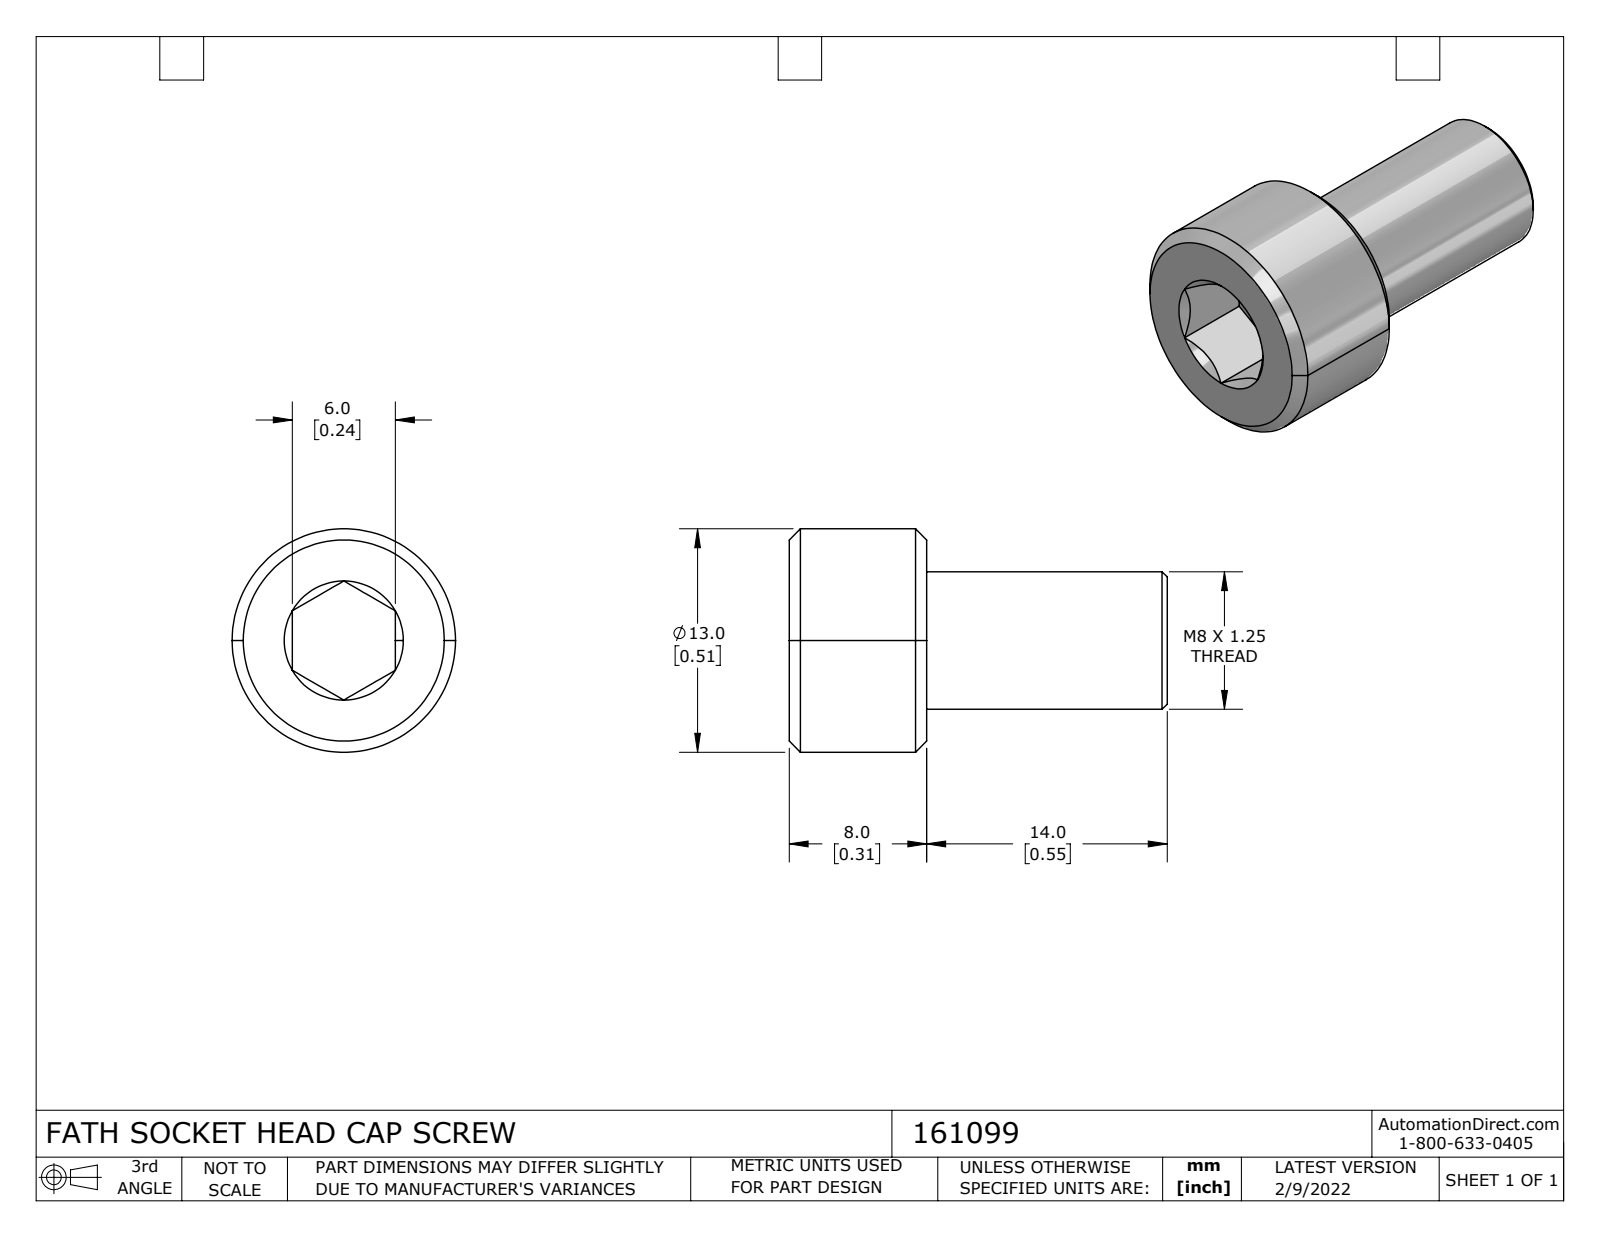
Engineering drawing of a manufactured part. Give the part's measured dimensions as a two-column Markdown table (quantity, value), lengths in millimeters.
| quantity | value |
| --- | --- |
| part name | 161099 |
| STEP written by | SolidWorks 2021 (CONFIG_CONTROL_DESIGN) |
| units | millimeters |
| bodies | 1 solid, 27 faces (10 planar, 4 cylindrical, 13 other) |
| overall size | 22 × 13 × 13 |
| volume | 1 606 mm³ |
| surface area | 997 mm² |
| round bosses / shafts (diameter × count) | 13 × 1, 8 × 1 |
| main face-to-face distances | 8, 6, 22, 14, 4.5, 3.5, 17.5 |
